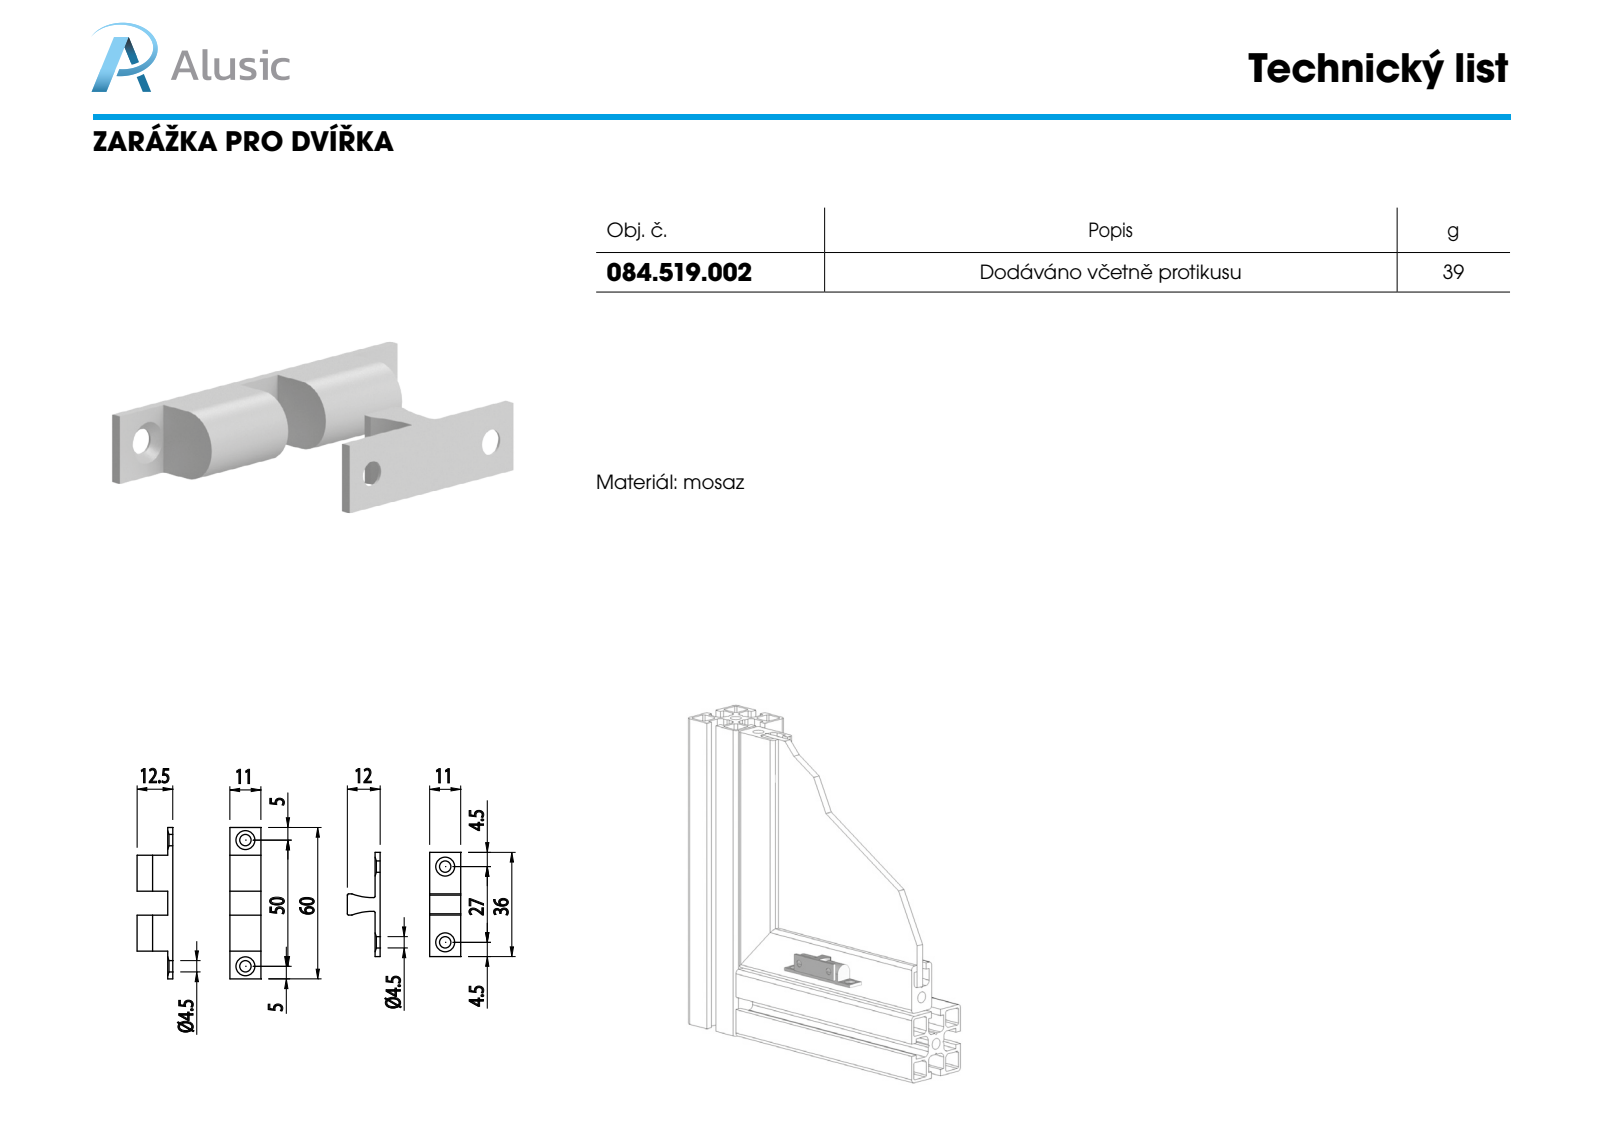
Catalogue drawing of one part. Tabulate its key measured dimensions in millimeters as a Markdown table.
| quantity | value |
| --- | --- |
| part name | 084.519.002 |
| STEP written by | SolidWorks 2011 (CONFIG_CONTROL_DESIGN) |
| units | millimeters |
| bodies | 6 solids, 58 faces (30 planar, 12 cylindrical, 16 other) |
| overall size | 60 × 15 × 11 |
| volume | 5 563 mm³ |
| surface area | 4 131 mm² |
| round holes (diameter × count) | 4.5 × 2 |
| partial cylindrical surfaces (radius × count) | 0.36 × 2, 12 × 2, 5.5 × 1 |
| main face-to-face distances | 11, 15, 14, 23.5, 1.5, 13.5, 12.5, 2.5, 37.5, 9.5 |
| hole center spacings | 49 |
